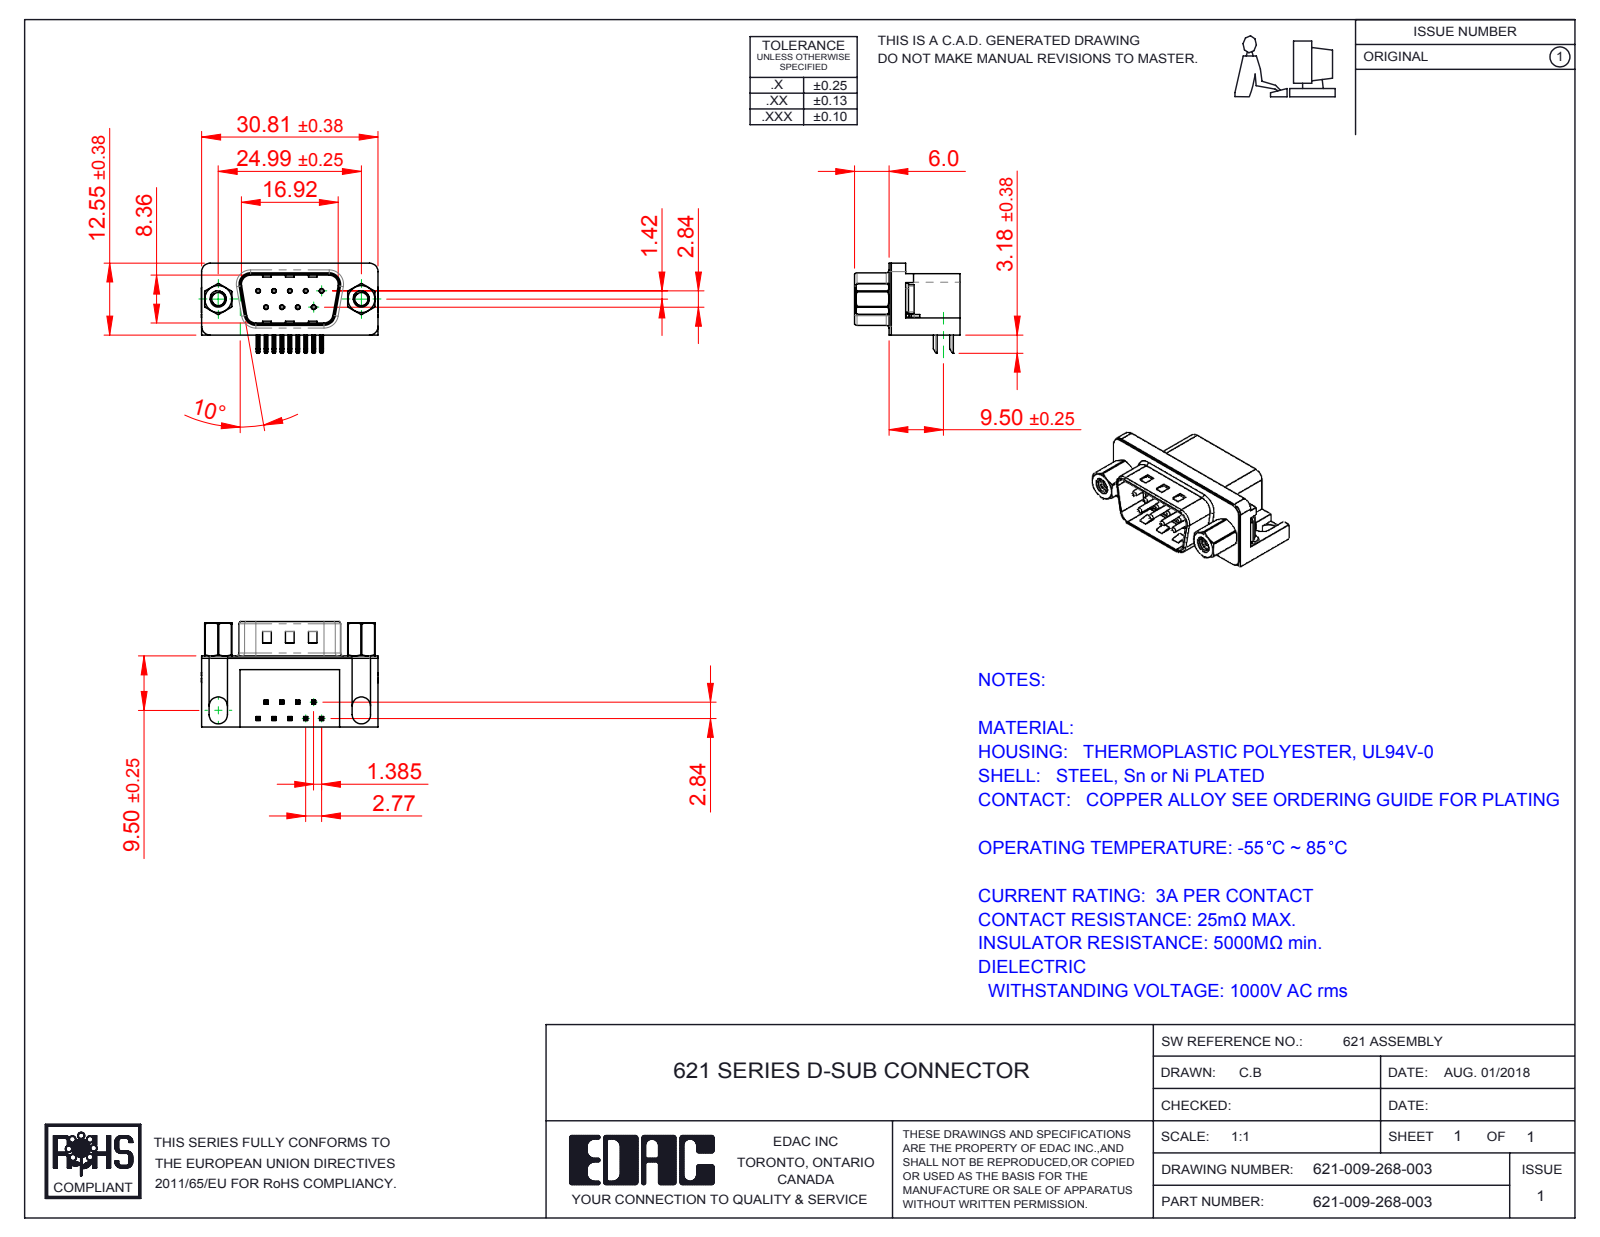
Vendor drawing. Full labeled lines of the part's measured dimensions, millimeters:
Part name (STEP PRODUCT): 621 4-40 Threaded Rivet; 621-009-268-003; 621 4-40 Hex Standoff 5; 621 Contact Top (+4 more)
STEP written by: SolidWorks 2016 (CONFIG_CONTROL_DESIGN)
Units: millimetres
Bodies: 17 solids, 1111 faces (593 planar, 383 cylindrical, 135 other)
Overall size (bounding box): 30.89 × 18.4 × 15.73
Volume: 3 423 mm³ · Surface area: 4 731 mm²
Round holes (diameter × count): ⌀0.35 ×9, ⌀0.8 ×9, ⌀2.26 ×2, ⌀2.29 ×2, ⌀4 ×2, ⌀4.8 ×2, ⌀5 ×2
Round bosses / shafts (diameter × count): ⌀0.75 ×9, ⌀4.9 ×2, ⌀4.75 ×2, ⌀3.9 ×2, ⌀2.79 ×2
Partial cylindrical surfaces — rounded edges, fillets, slot ends (radius × count): R0.25 ×44, R0.12 ×18, R1 ×16, R0.5 ×9, R1.5 ×8, R1.6 ×8, R0.9 ×4, R2 ×4
Main face-to-face distances: 0.4, 12, 12.4, 10.35, 9.5, 2.5, 2.9, 2.1, 0.35, 10.7
Hole centre spacings: 3.16, 2.77, 5.54, 5.03, 5.04, 8.31, 7.48, 7.49
